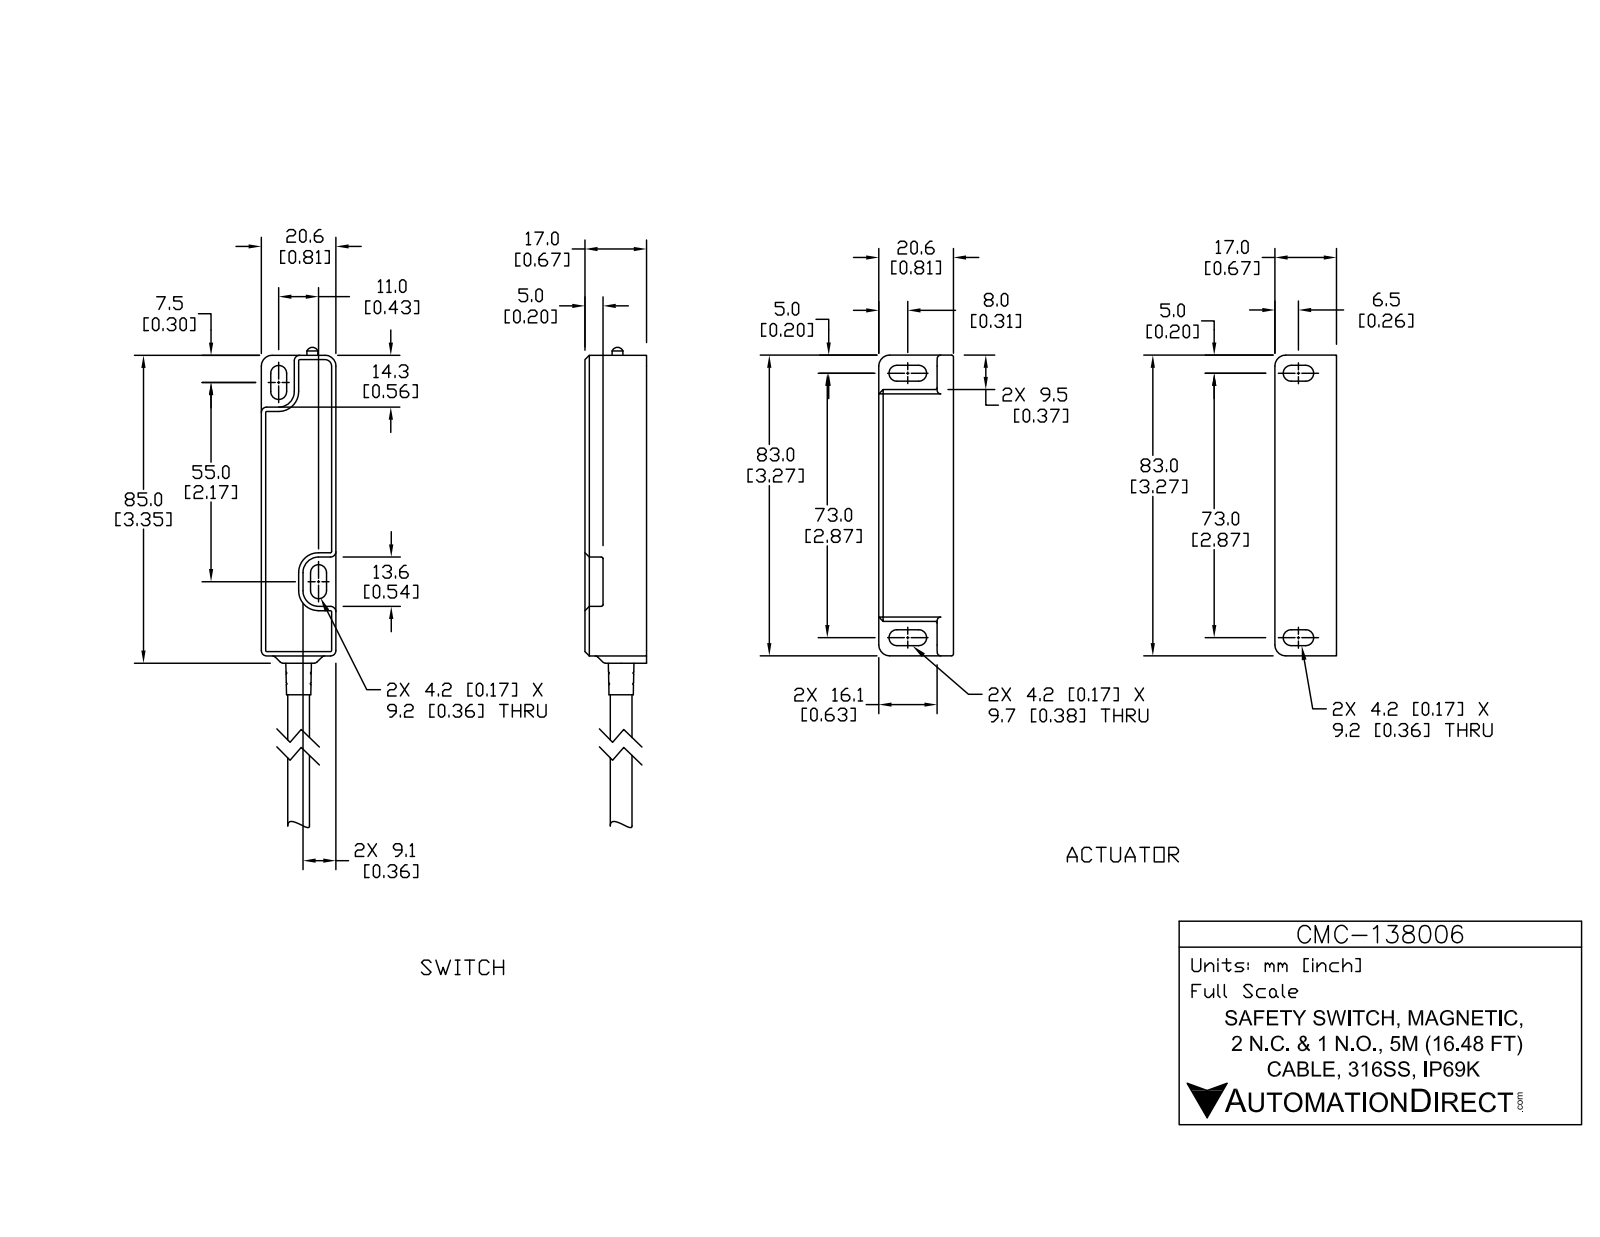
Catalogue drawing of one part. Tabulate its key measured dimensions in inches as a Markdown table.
| quantity | value |
| --- | --- |
| part name | CMC-138006; CMC-138006_2; CMC-138006_1 |
| STEP written by | SolidWorks 2017 (AUTOMOTIVE_DESIGN) |
| units | inches |
| bodies | 5 solids, 189 faces (58 planar, 66 cylindrical, 65 other) |
| overall size | 7.255 × 1.378 × 0.811 |
| volume | 3.331 in³ |
| surface area | 25.32 in² |
| round bosses / shafts (diameter × count) | 0.236 × 1, 0.118 × 1 |
| partial cylindrical surfaces (radius × count) | 0.02 × 15, 0.039 × 15, 0.083 × 8, 0.059 × 6, 0.087 × 4, 0.028 × 3, 0.118 × 3, 0.169 × 3 |
| main face-to-face distances | 0.709, 0.669, 0.811, 0.039, 1.378, 0.177, 0.374, 2.894, 3.268, 0.492 |
